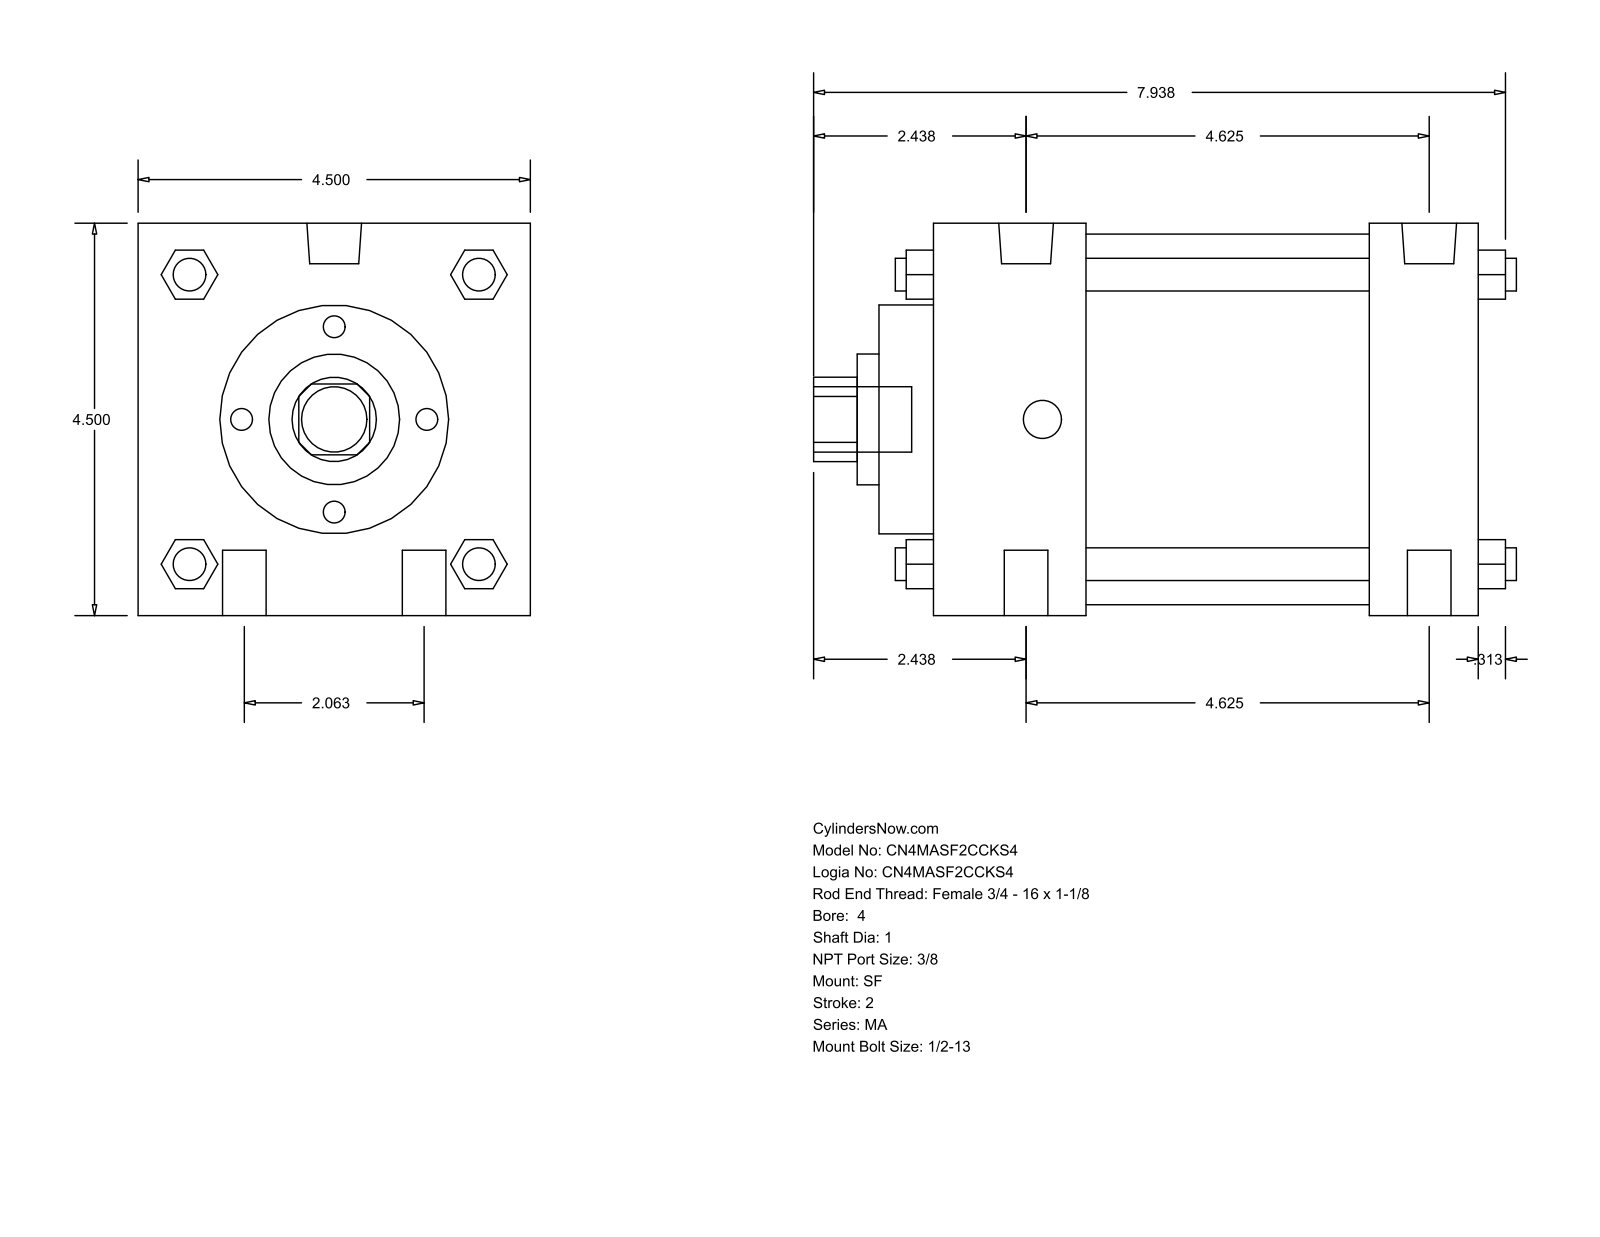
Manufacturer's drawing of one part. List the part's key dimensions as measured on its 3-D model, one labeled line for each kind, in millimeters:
Part name (STEP PRODUCT): MA_SF__0400_1
STEP written by: GSSL Pune (CONFIG_CONTROL_DESIGN)
Units: millimetres
Bodies: 0 solids, 126 faces (95 planar, 31 cylindrical, 0 other)
Overall size (bounding box): 204.79 × 114.3 × 114.3
Round holes (diameter × count): ⌀25.4 ×1, ⌀38.1 ×1, ⌀66.67 ×1, ⌀107.95 ×1
Round bosses / shafts (diameter × count): ⌀12.7 ×4, ⌀9.53 ×4, ⌀15.93 ×2, ⌀11.11 ×2, ⌀19.05 ×1
Partial cylindrical surfaces — rounded edges, fillets, slot ends (radius × count): R12.29 ×1
Main face-to-face distances: 114.3, 158.76, 127.01, 31.75, 44.46, 82.55, 15.87, 60.33, 142.88, 174.63
